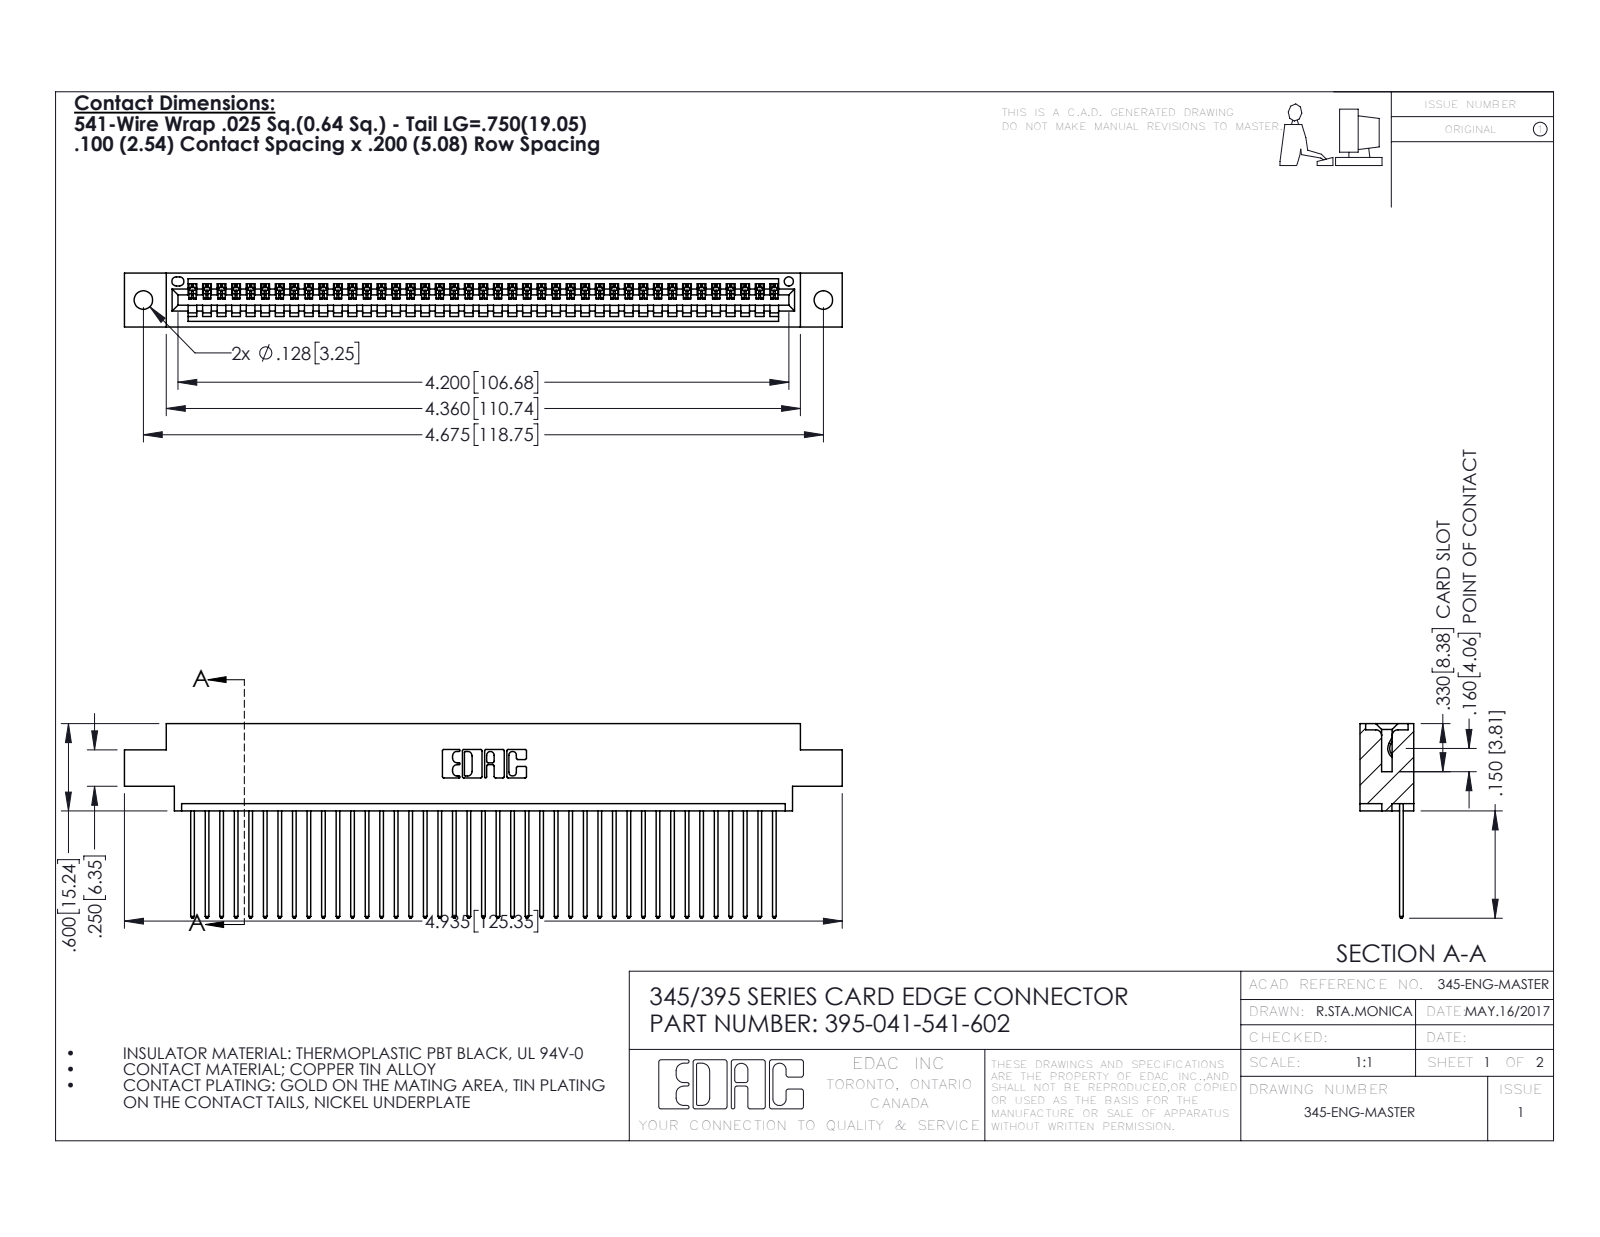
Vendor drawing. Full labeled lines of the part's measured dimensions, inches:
Part name (STEP PRODUCT): 345-292-001_345-293-141; 395-041-541-602; 345 Part_0.170 Offset - 0.128 Dia
STEP written by: SolidWorks 2016 (CONFIG_CONTROL_DESIGN)
Units: inches
Bodies: 42 solids, 2508 faces (1724 planar, 784 cylindrical, 0 other)
Overall size (bounding box): 4.935 × 1.337 × 0.37
Volume: 0.725 in³ · Surface area: 25.46 in²
Round holes (diameter × count): ⌀0.128 ×2, ⌀0.064 ×1
Partial cylindrical surfaces — rounded edges, fillets, slot ends (radius × count): R0.006 ×82, R0.01 ×82, R0.01 ×22, R0.007 ×6, R0.031 ×6, R0.026 ×3, R0.031 ×2, R0.04 ×2
Main face-to-face distances: 0.072, 0.298, 0.37, 0.098, 0.272, 0.025, 0.2, 0.225, 0.175, 0.149
Hole centre spacings: 0.27, 4.439, 4.675
